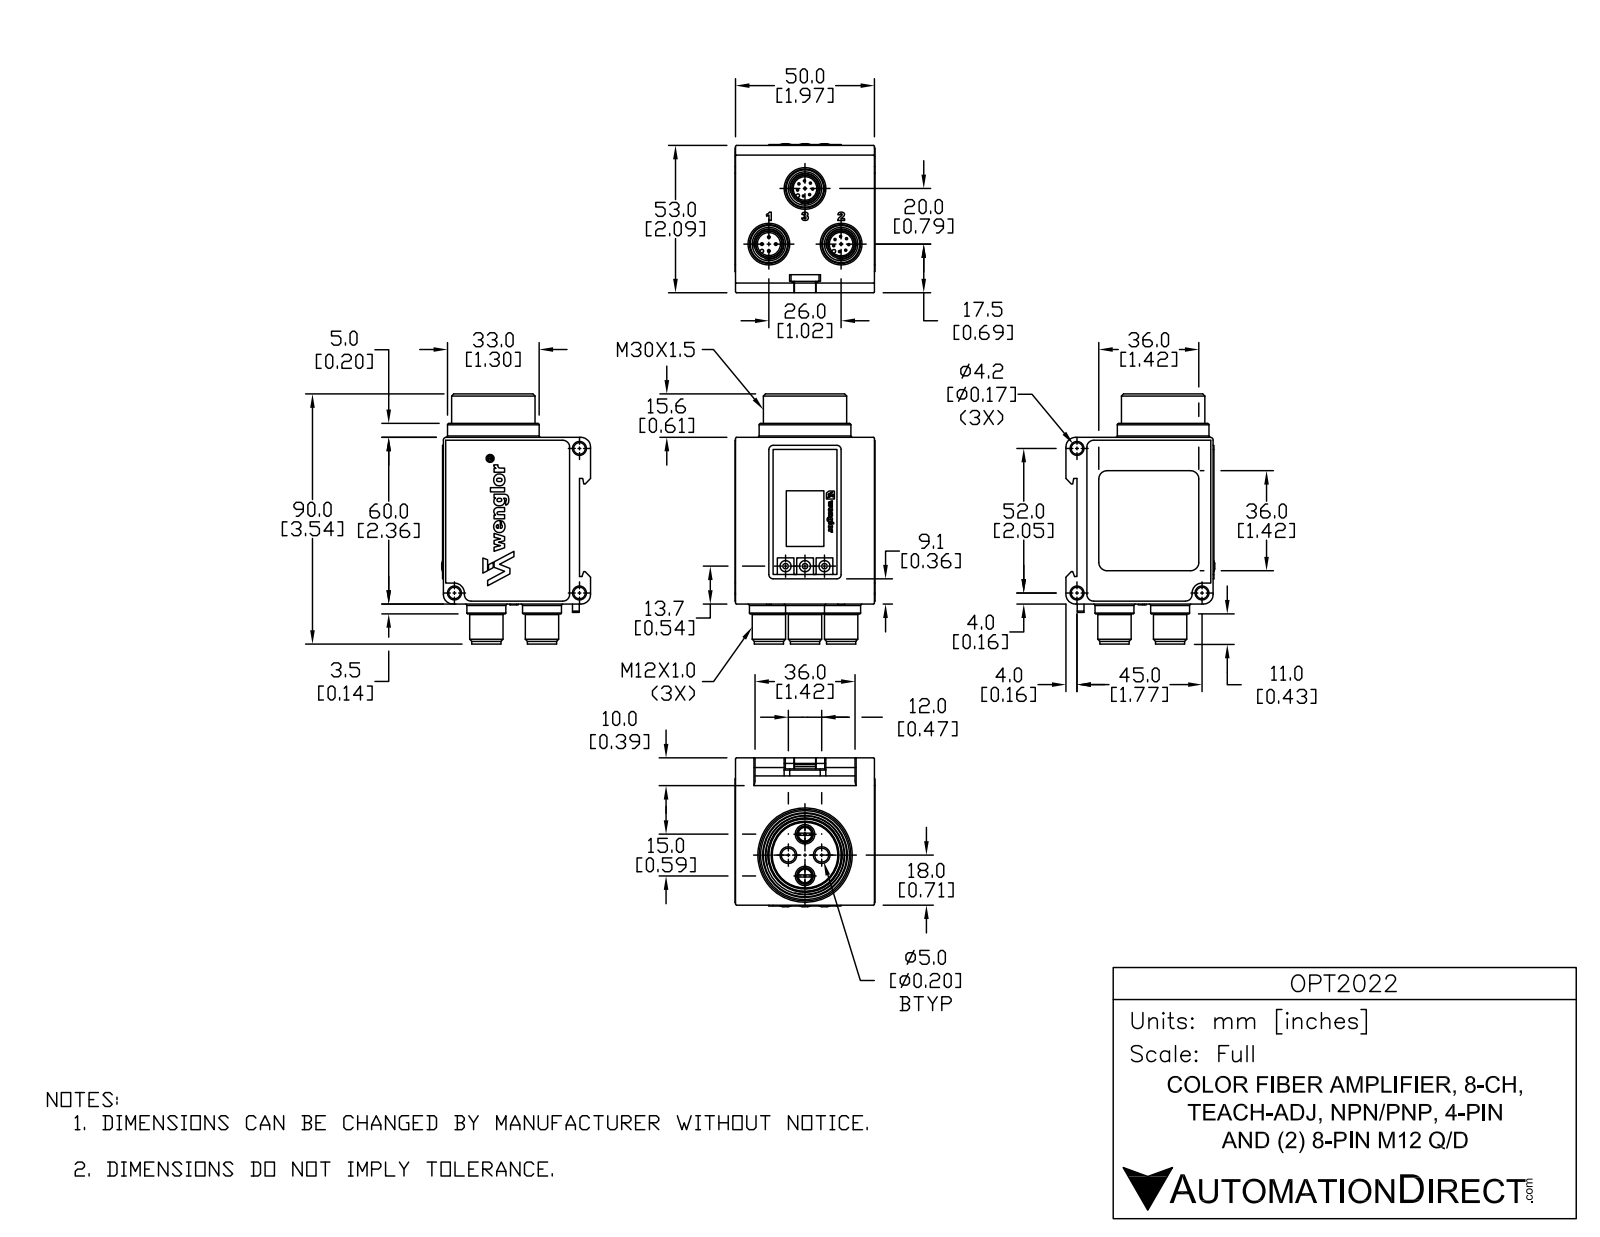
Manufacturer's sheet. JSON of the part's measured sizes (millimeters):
{"part_name": "1017997", "step_written_by": "Unknown (AUTOMOTIVE_DESIGN)", "units": "millimeters", "bodies": {"solids": 1, "faces": 681, "planar": 321, "cylindrical": 187, "other": 173}, "overall_size": [89.8, 53.6, 50.4], "volume_mm3": 159531, "surface_area_mm2": 26934, "round_holes": [[4.2, 3], [9.55, 3], [5, 2], [6, 2], [8.5, 2], [3.5, 1], [4.4, 1], [8.3, 1], [26.4, 1]], "round_bosses_or_shafts": [[0.8, 16], [1, 4], [14, 3], [12, 3], [10.5, 3], [9.4, 3], [8, 3], [33, 1]], "partial_cylinders_radius": [[0.4, 59], [0.75, 9], [3, 9], [3.5, 6], [2.25, 5], [1.5, 4], [0.6, 3], [1, 3]], "face_to_face_distances": [46.5, 50.3, 50.4, 60, 46.8, 50.2, 2.5, 49, 49.3, 50.1], "hole_center_spacings": [9.6, 6, 6.5, 7.5, 16.4, 18.85, 21.8, 23.85]}
